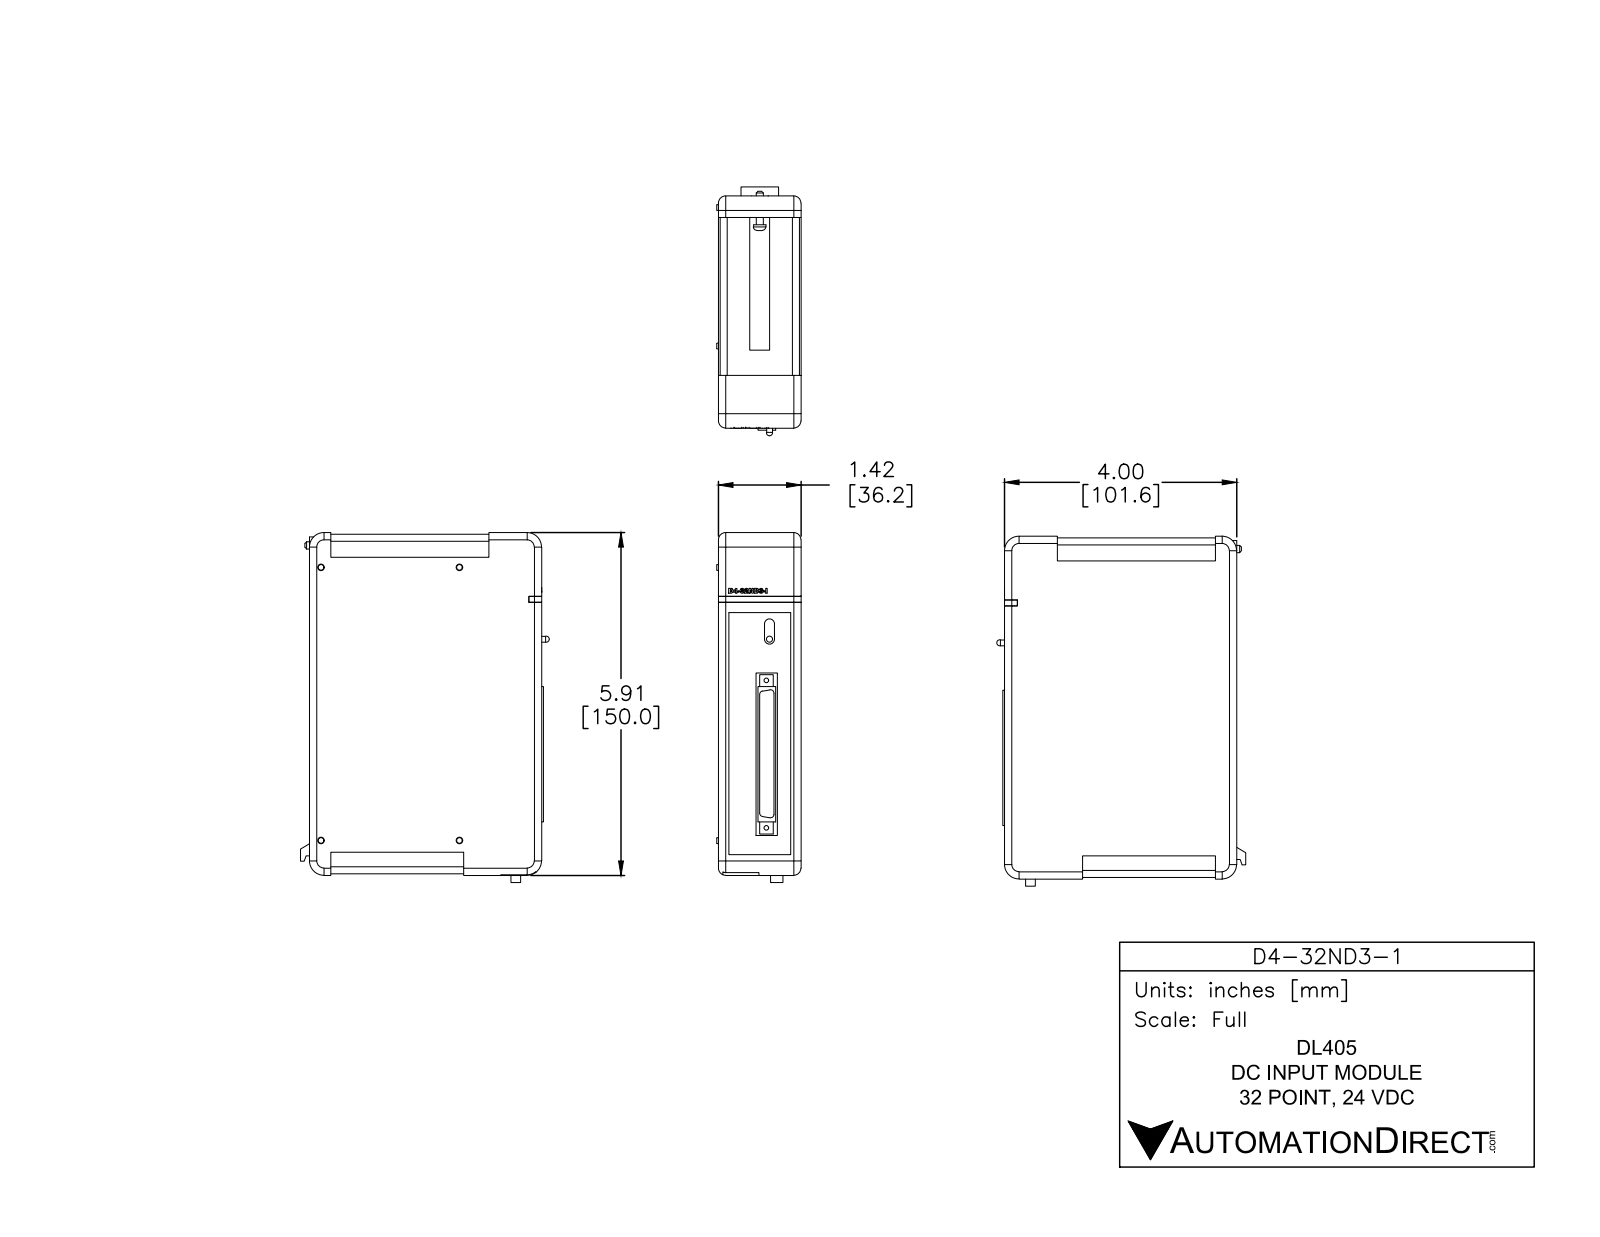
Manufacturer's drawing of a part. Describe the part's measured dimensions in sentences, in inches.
The part is named "D4-32ND3-1". Its 3-D file was written by "SolidWorks 2014 (AUTOMOTIVE_DESIGN)". It is 2 solids with 321 faces: 200 planar, 46 cylindrical and 75 other. Overall it measures 6.025 by 4.285 by 1.455 inches. Its volume is 32.07 cubic inches and its surface area 83.59 square inches. Round holes: 2 of diameter 0.08. Round bosses or shafts: 1 of diameter 0.212, 1 of diameter 0.123, 1 of diameter 0.1. Partial cylindrical surfaces (rounded edges, fillets, slot ends): 8 of radius 0.125, 4 of radius 0.06, 4 of radius 0.12, 4 of radius 0.25, 2 of radius 0.085, 1 of radius 0.145, 1 of radius 0.171. The main face-to-face distances are 1.425, 0.03, 3.97, 1.395, 5.845, 5.875, 4, 0.2, 3.77, 3.8. The hole center spacings are 2.538.
